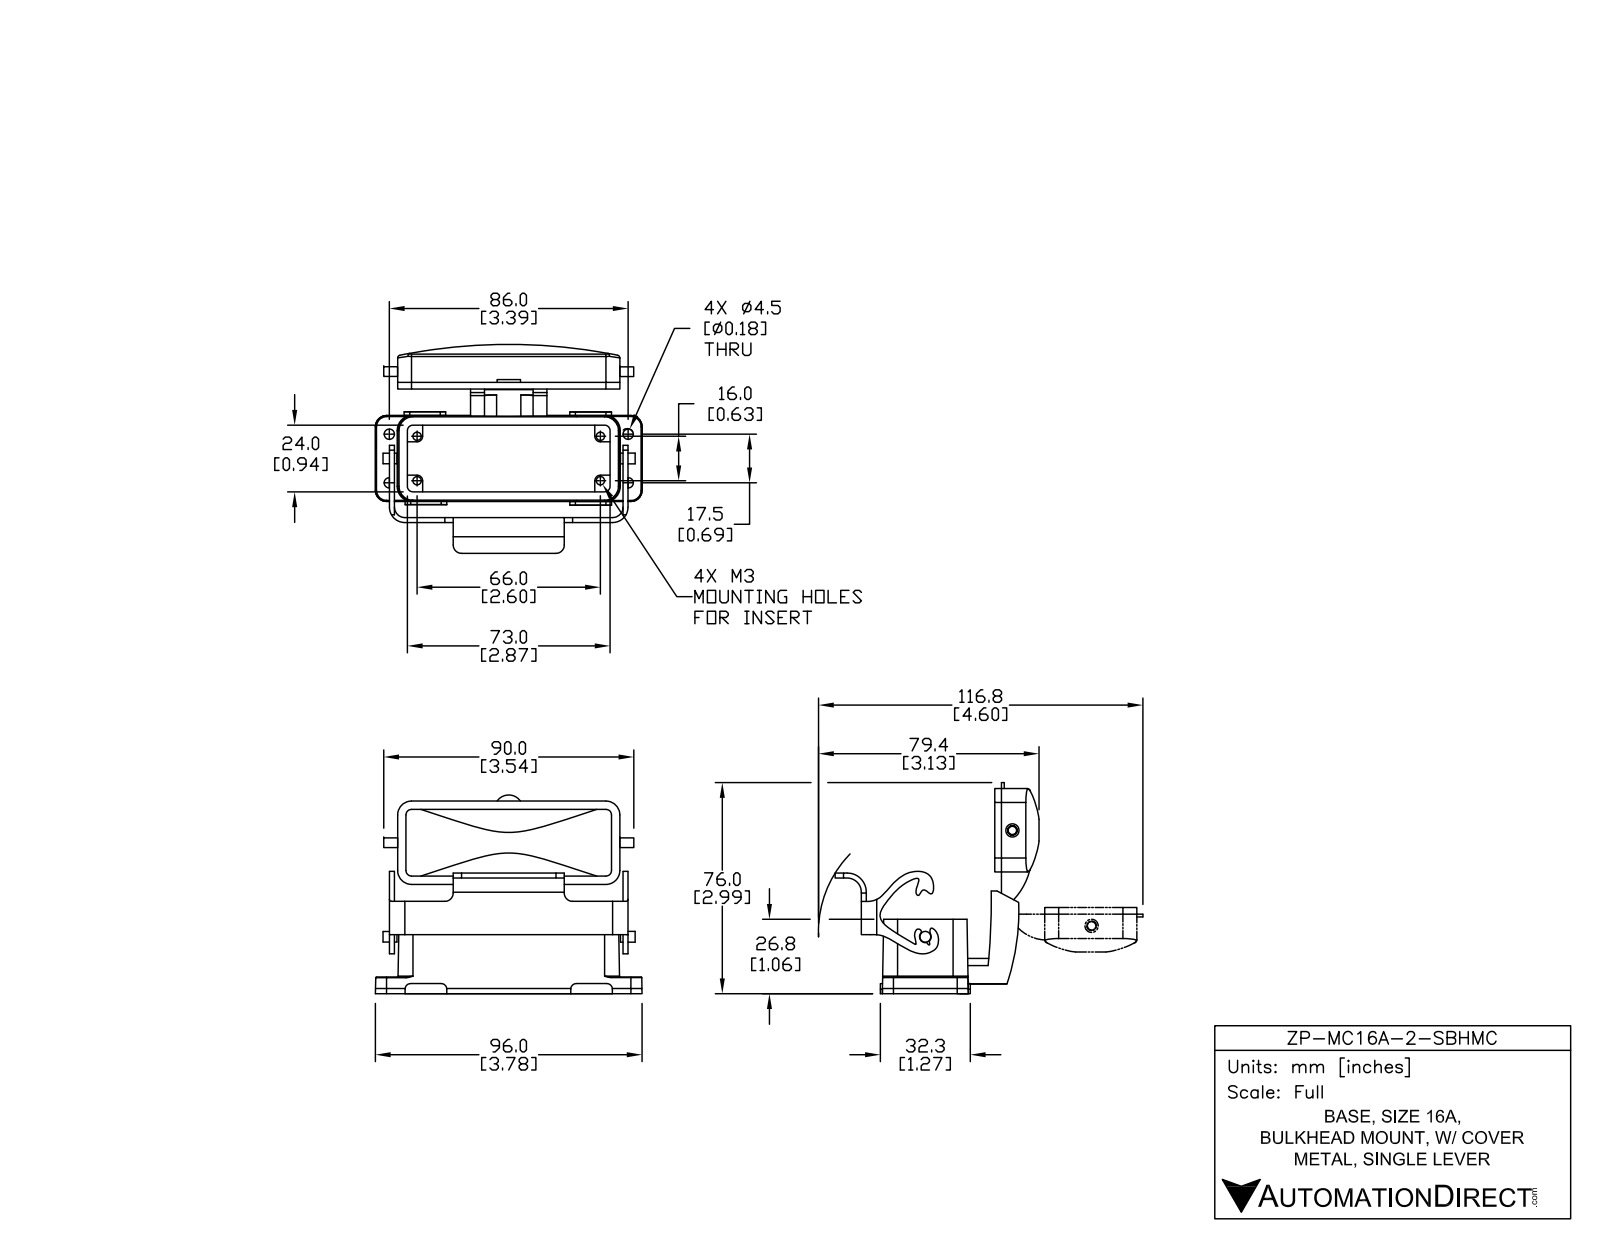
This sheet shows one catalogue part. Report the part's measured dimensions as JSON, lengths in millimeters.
{"part_name": "ZP-MC16A-2-SBHMC", "step_written_by": "SolidWorks 2014 (AUTOMOTIVE_DESIGN)", "units": "millimeters", "bodies": {"solids": 6, "faces": 339, "planar": 152, "cylindrical": 109, "other": 78}, "overall_size": [96, 76.3, 75.2], "volume_mm3": 47233, "surface_area_mm2": 33632, "round_holes": [[3, 4], [3.7, 4]], "round_bosses_or_shafts": [[7.5, 1], [4.95, 1], [3.9, 1], [3.8, 1], [3.4, 1]], "partial_cylinders_radius": [[2, 18], [5, 8], [0.3, 5], [1, 4], [3, 4], [0.25, 3], [3.75, 2], [5.55, 2]], "face_to_face_distances": [3, 27, 1.8, 44.13, 47.13, 74.13, 30, 71.13, 24, 46.25], "hole_center_spacings": [10.03, 19.51, 76, 77.82, 16, 17.5, 66, 67.91]}
